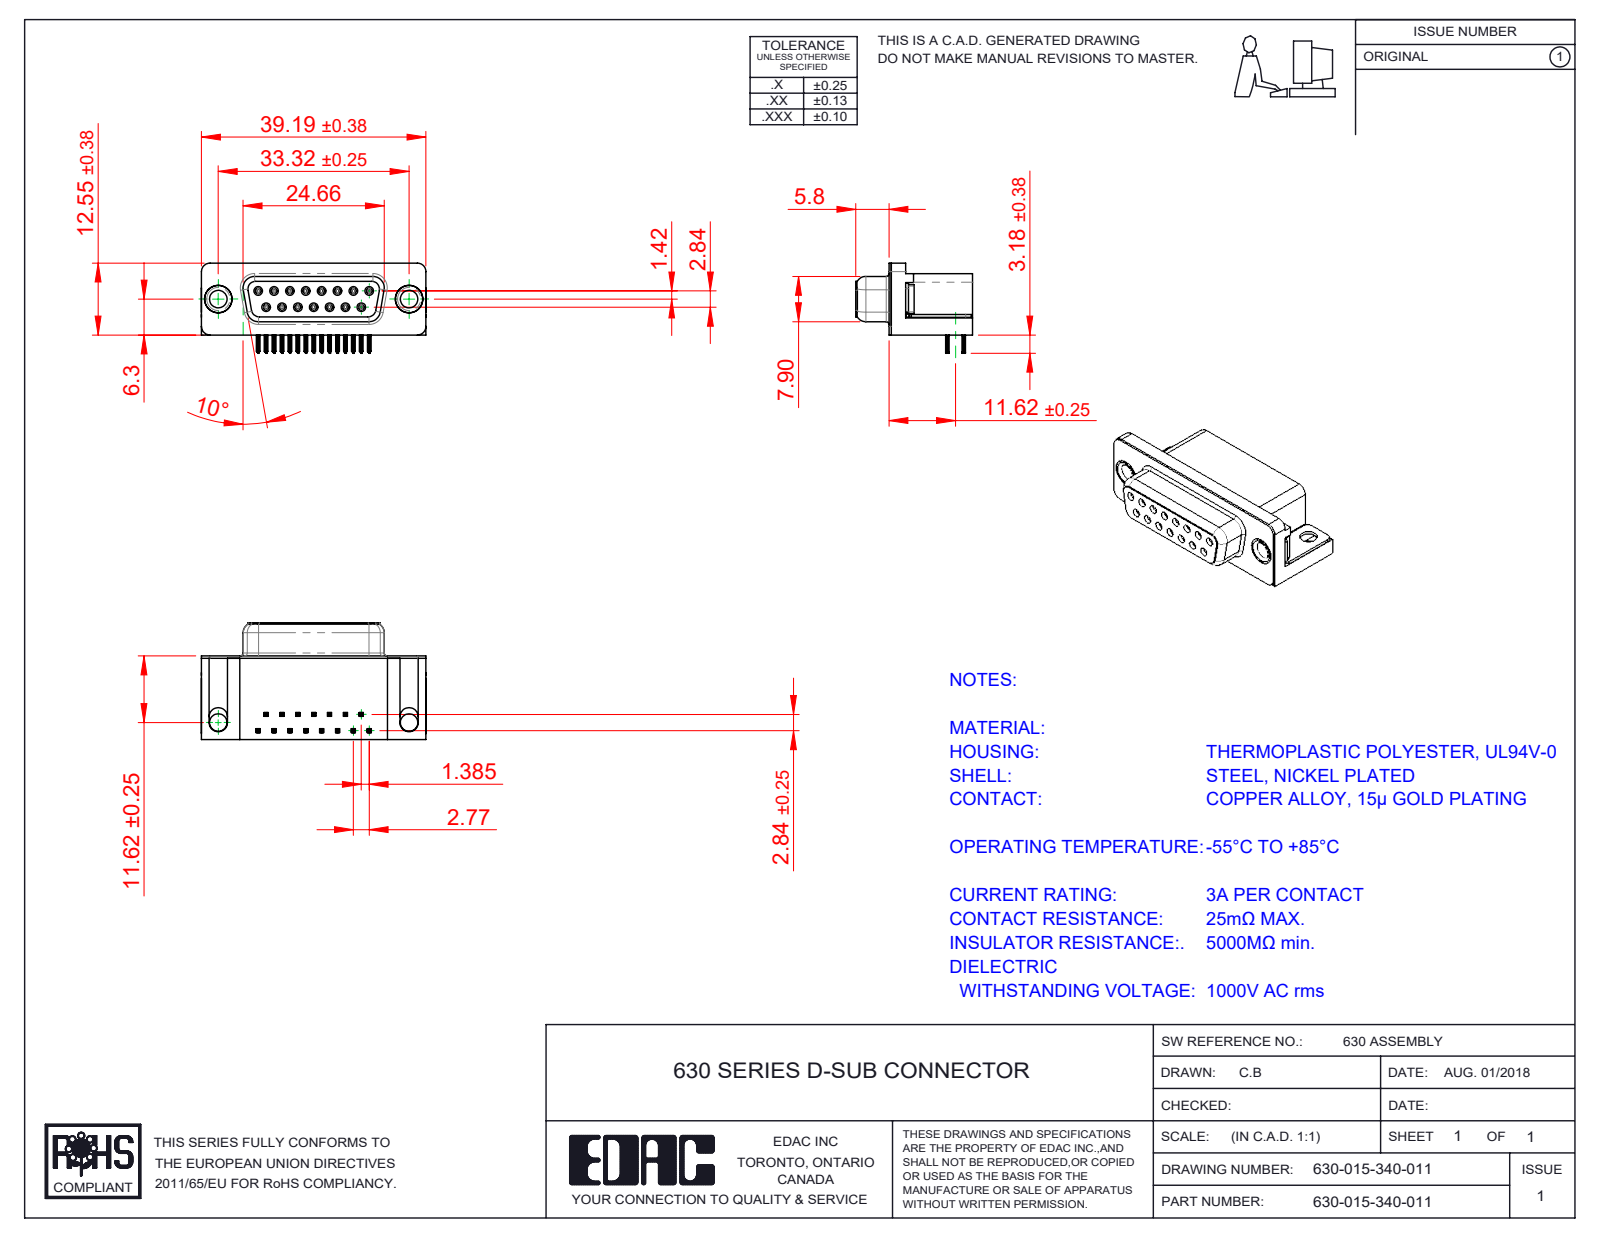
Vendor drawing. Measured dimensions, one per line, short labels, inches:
name: 630 Contact Top; 630-015-340-011; 630 Thru Hole Board Mount; 630 Shell_15 Socket (+3 more)
written by: SolidWorks 2020 (CONFIG_CONTROL_DESIGN)
unit: in
bodies: 21 solids, 2385 faces (1072 planar, 587 cylindrical, 726 other)
size: 1.544 × 0.803 × 0.619
volume: 0.357 in³; area: 11.07 in²
holes: 15× ⌀0.031, 15× ⌀0.035, 4× ⌀0.12, 2× ⌀0.157, 2× ⌀0.189, 2× ⌀0.197
bosses: 15× ⌀0.047, 2× ⌀0.193, 2× ⌀0.187, 2× ⌀0.152
rounds: 120× R0.004, 60× R0.006, 30× R0.014, 18× R0.039, 15× R0.013, 8× R0.01, 8× R0.053, 8× R0.059
face distances: 0.016, 0.559, 0.107, 0.244, 0.407, 0.575, 0.114, 0.228, 0.125, 0.262
hole spacings: 0.124, 0.109, 0.218, 0.198, 0.198, 0.294, 0.295, 0.327
